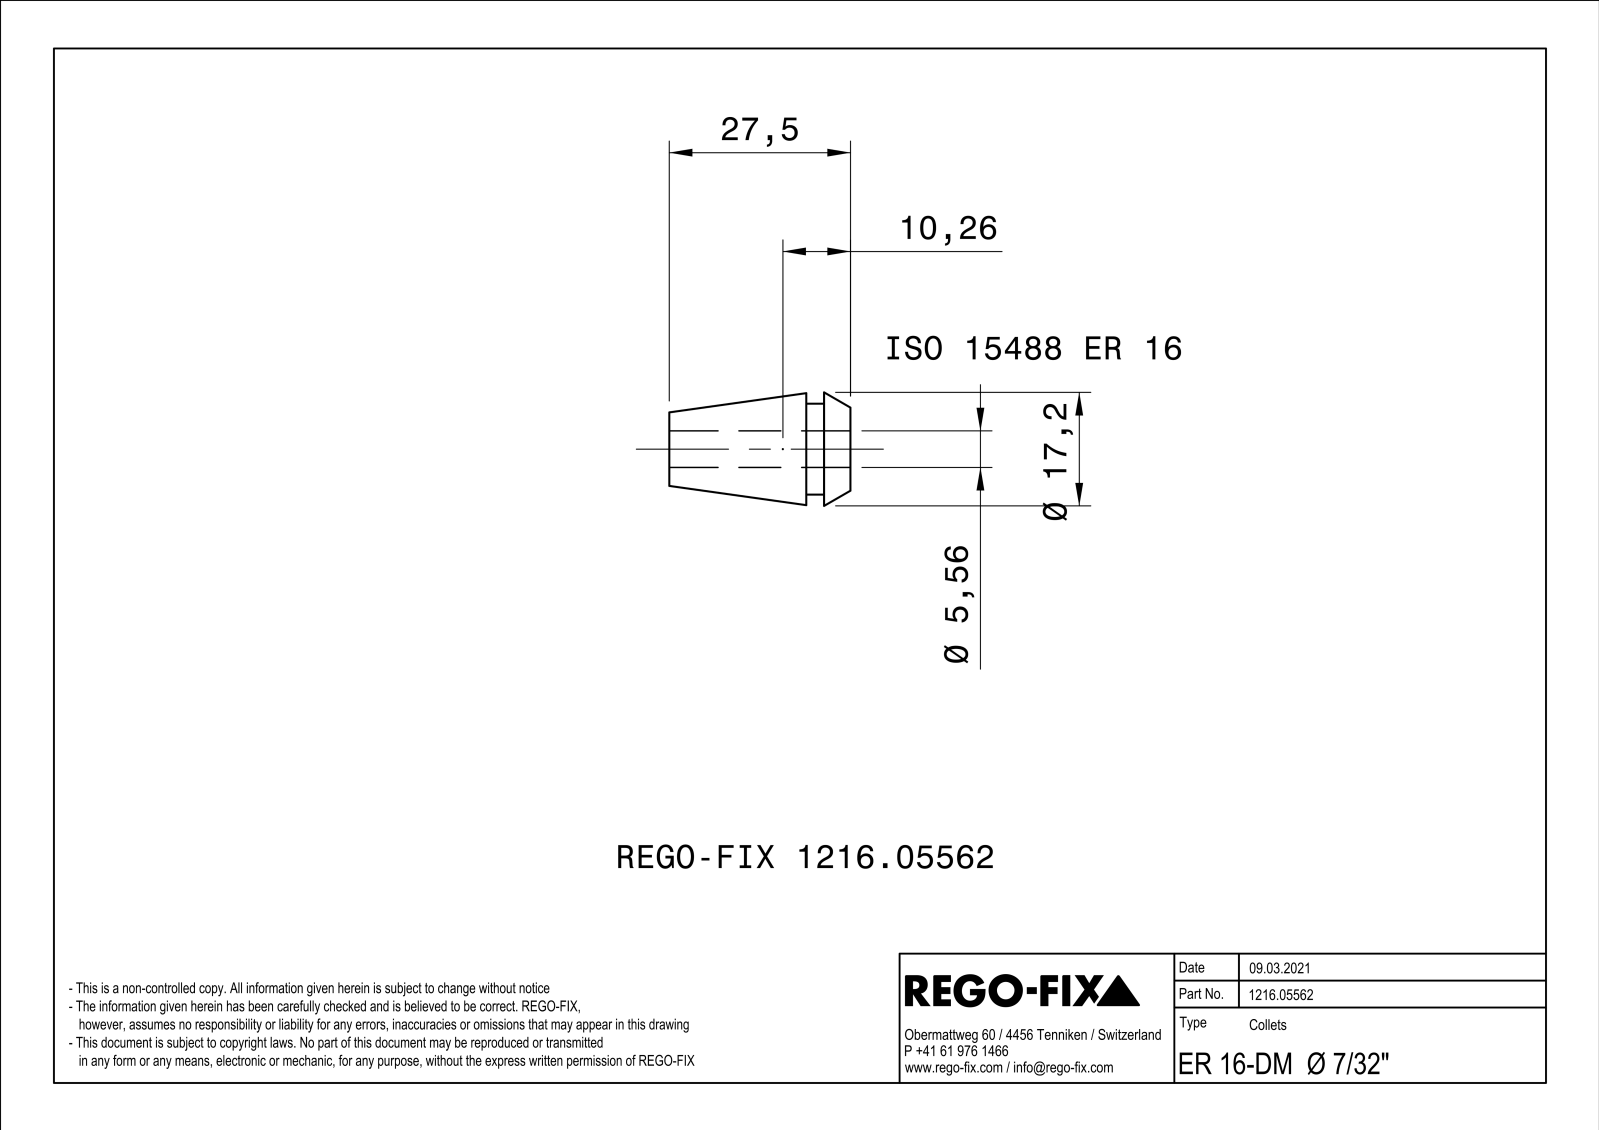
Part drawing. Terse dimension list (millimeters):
name: NOCUT
written by: SIEMENS PLM Software Solid Edge ST10 (AUTOMOTIVE_DESIGN)
unit: mm
bodies: 1 solid, 146 faces (80 planar, 9 cylindrical, 57 other)
size: 27.5 × 17.24 × 17.24
volume: 3 095 mm³; area: 4 294 mm²
holes: 1× ⌀5.56
bosses: 1× ⌀13.8
face distances: 0.5, 4, 6.7, 2.7, 27.5, 23.5, 20.8, 13, 9, 6.3
